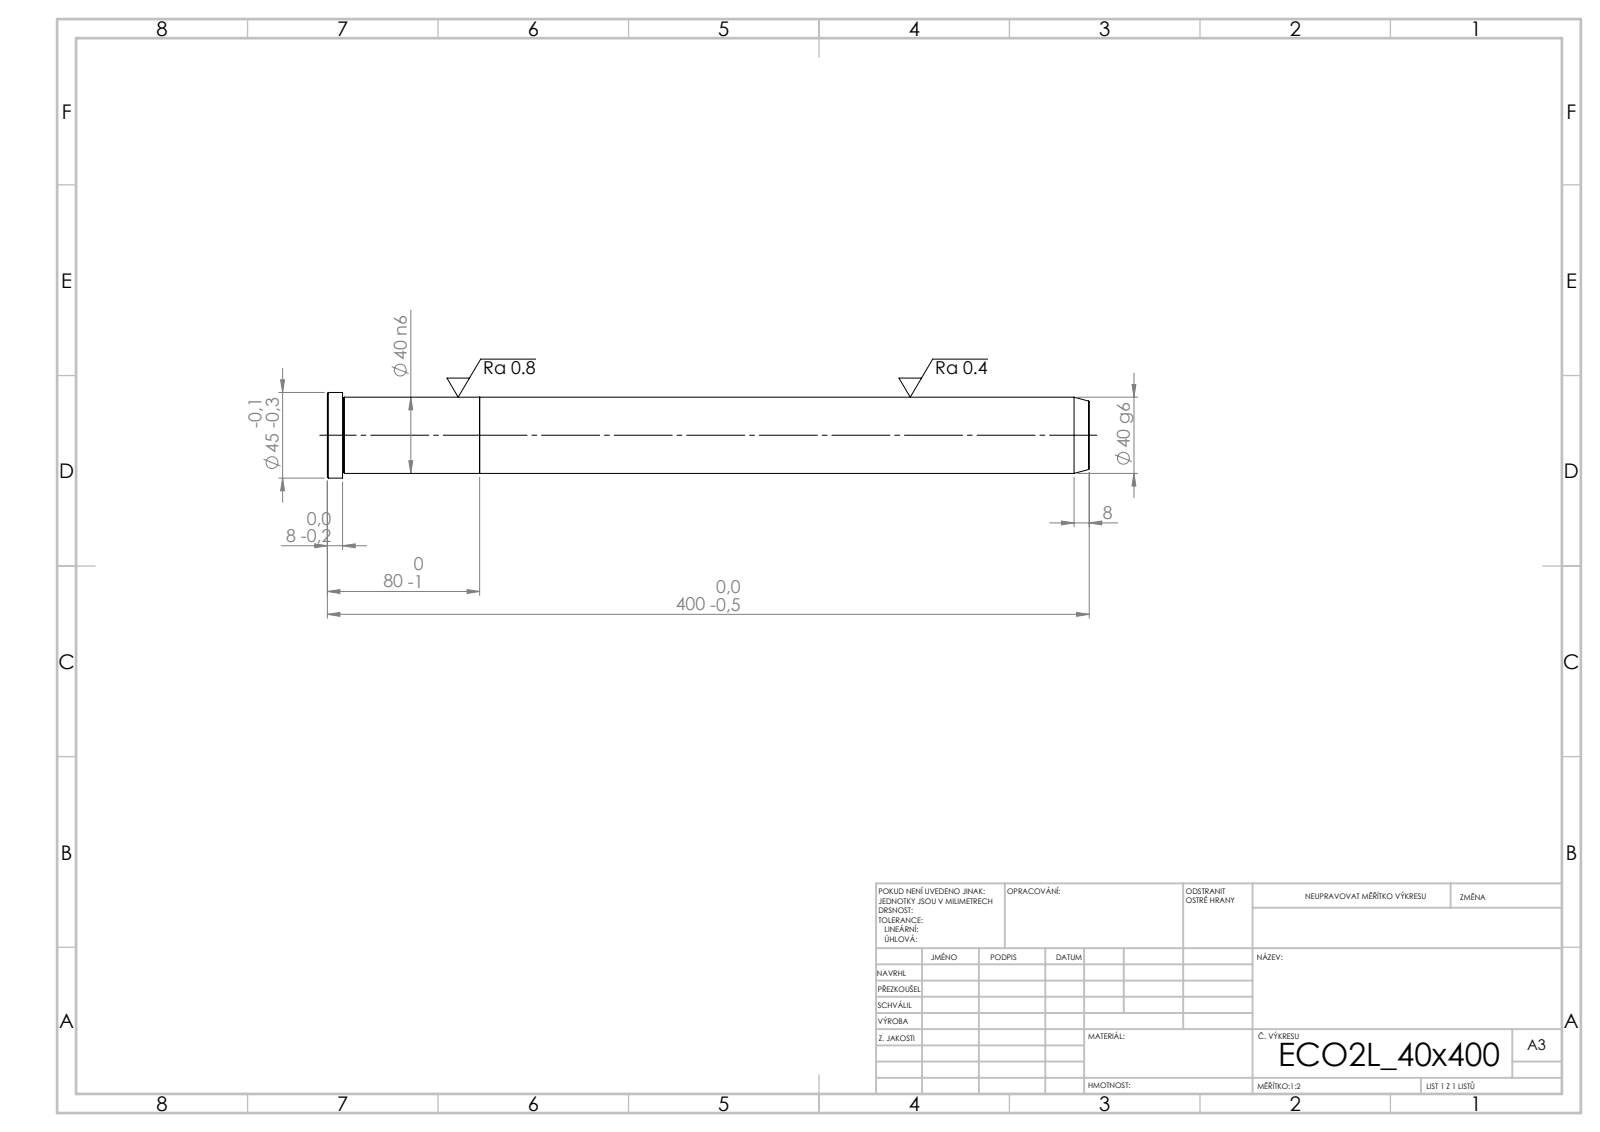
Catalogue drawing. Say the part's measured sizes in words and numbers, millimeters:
Its 3-D file was written by "SolidWorks 2019 (CONFIG_CONTROL_DESIGN)". It is 2 solids with 21 faces: 5 planar, 6 cylindrical and 10 other. Overall it measures 400 by 45 by 45 millimeters. Its volume is 504 217 cubic millimeters and its surface area 55 824 square millimeters. Round bosses or shafts: 1 of diameter 45, 1 of diameter 40. The main face-to-face distances are 80, 320, 400, 392, 72, 8.
